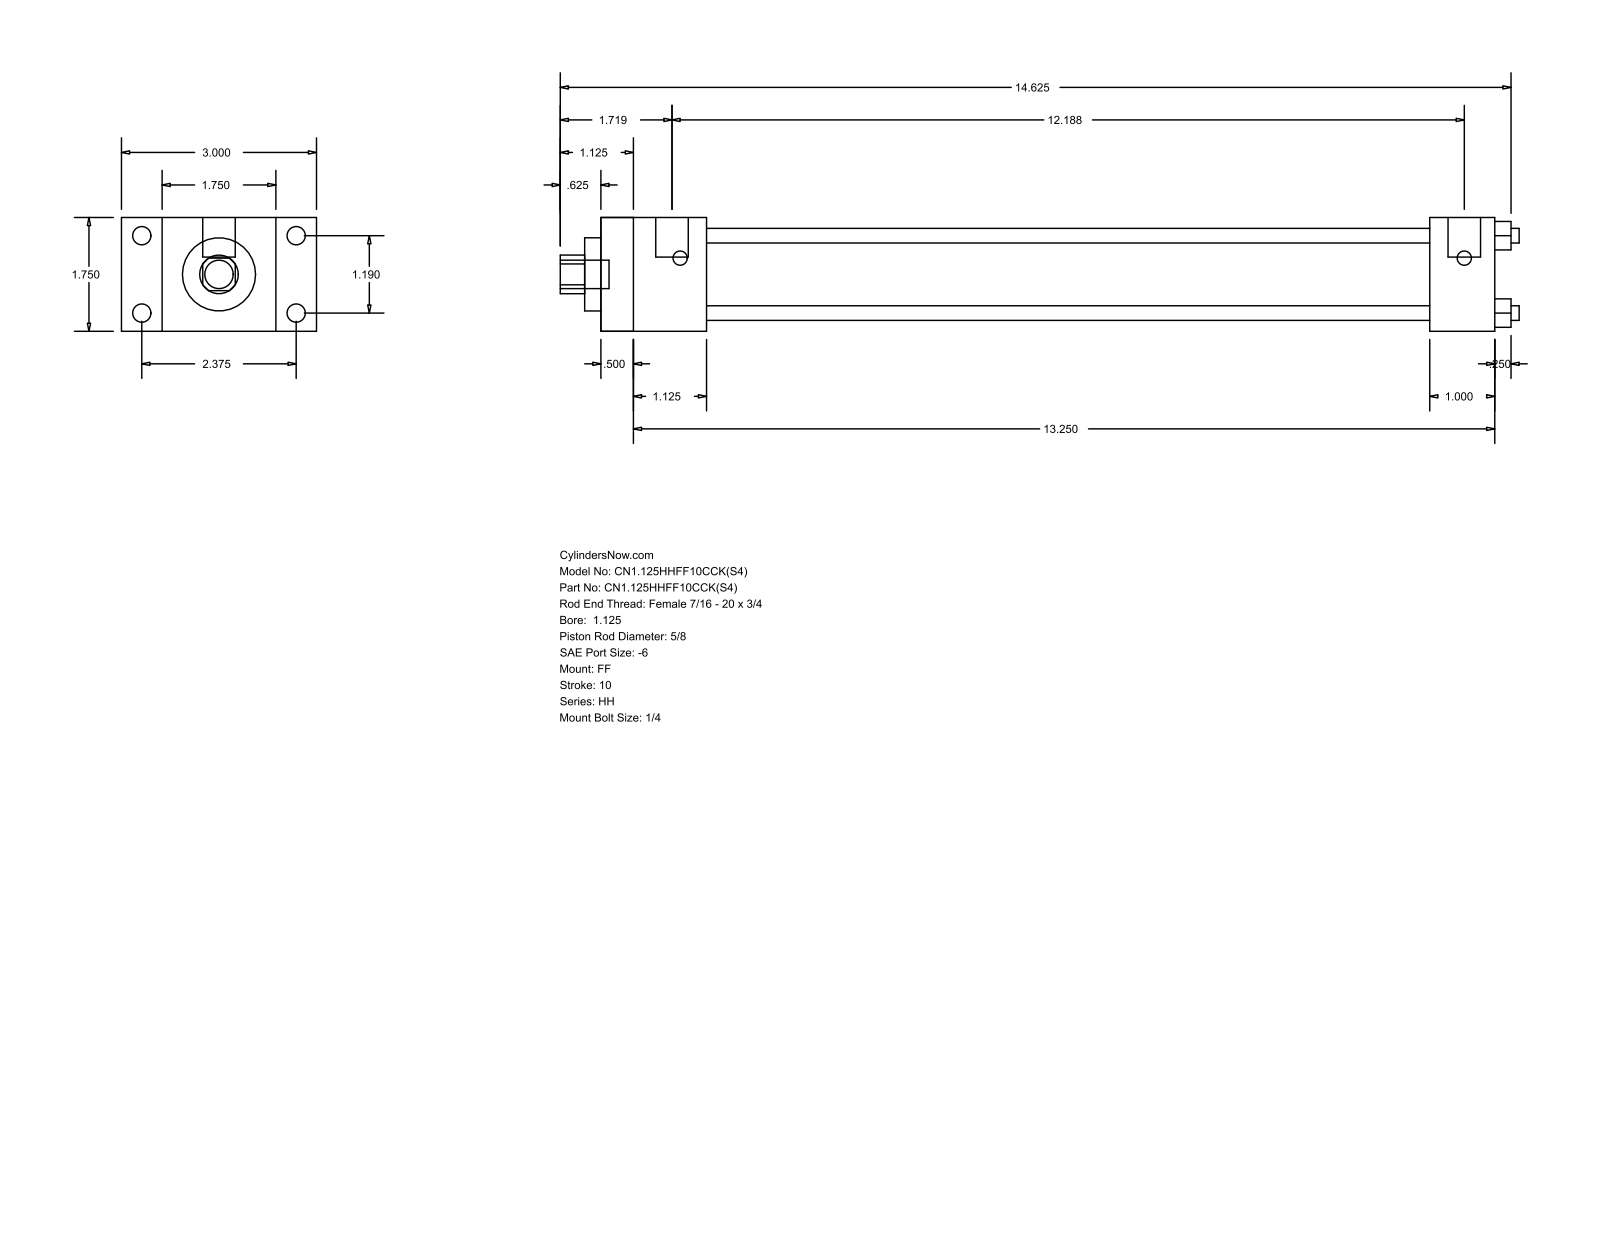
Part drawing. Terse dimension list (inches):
name: HH_FF__0112_0.625
written by: GSSL Pune (CONFIG_CONTROL_DESIGN)
unit: in
bodies: 0 solids, 92 faces (64 planar, 28 cylindrical, 0 other)
size: 14.75 × 3 × 1.75
holes: 4× ⌀0.225, 1× ⌀0.625, 1× ⌀1.125, 1× ⌀1.375
bosses: 4× ⌀0.281, 4× ⌀0.219, 2× ⌀0.5, 1× ⌀0.437
rounds: 1× R0.297
face distances: 1.75, 13.75, 0.5, 13.25, 0.625, 2.375, 1.125, 1.625, 12.75, 12.25
hole spacings: 0.841, 1.19, 1.683
